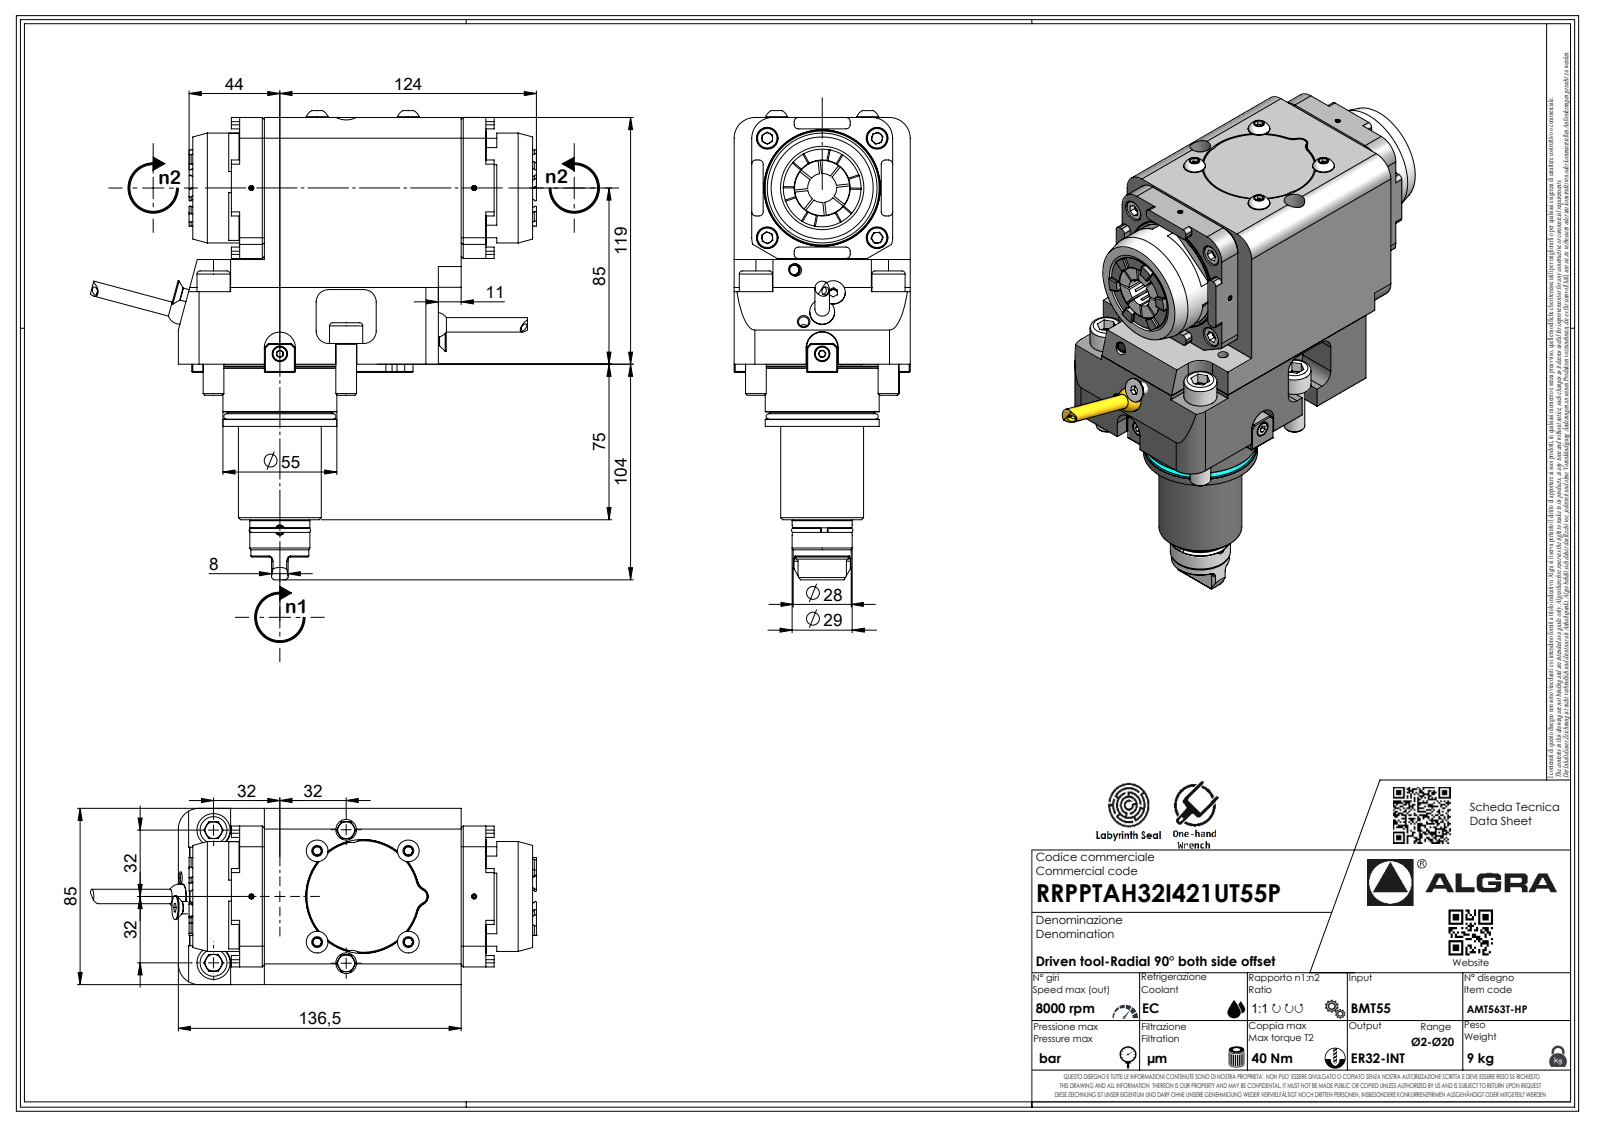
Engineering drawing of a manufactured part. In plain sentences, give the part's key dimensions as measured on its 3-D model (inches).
The part is named "RRPPTAH32I421UT55P". Its 3-D file was written by "SolidWorks 2023 (AUTOMOTIVE_DESIGN)". It is 1 solid with 757 faces: 508 planar, 125 cylindrical and 124 other. Overall it measures 8.909 by 6.732 by 3.346 inches. Its volume is 86.78 cubic inches and its surface area 163.1 square inches. Round holes: 2 of diameter 0.197, 2 of diameter 0.472, 1 of diameter 0.083, 1 of diameter 0.337, 1 of diameter 0.346. Round bosses or shafts: 4 of diameter 0.413, 4 of diameter 0.394, 2 of diameter 0.63, 1 of diameter 2.165, 1 of diameter 2.15, 1 of diameter 2.087, 1 of diameter 1.976, 1 of diameter 1.575. Partial cylindrical surfaces (rounded edges, fillets, slot ends): 22 of radius 0.079, 10 of radius 0.394, 7 of radius 0.013, 7 of radius 0.02, 7 of radius 0.146, 4 of radius 0.157, 2 of radius 0.039, 2 of radius 0.325. The main face-to-face distances are 3.346, 4.685, 0.886, 1.358, 5.571, 5.098, 4.213, 0.472, 2.677, 3.012. The hole center spacings are 0.472.
